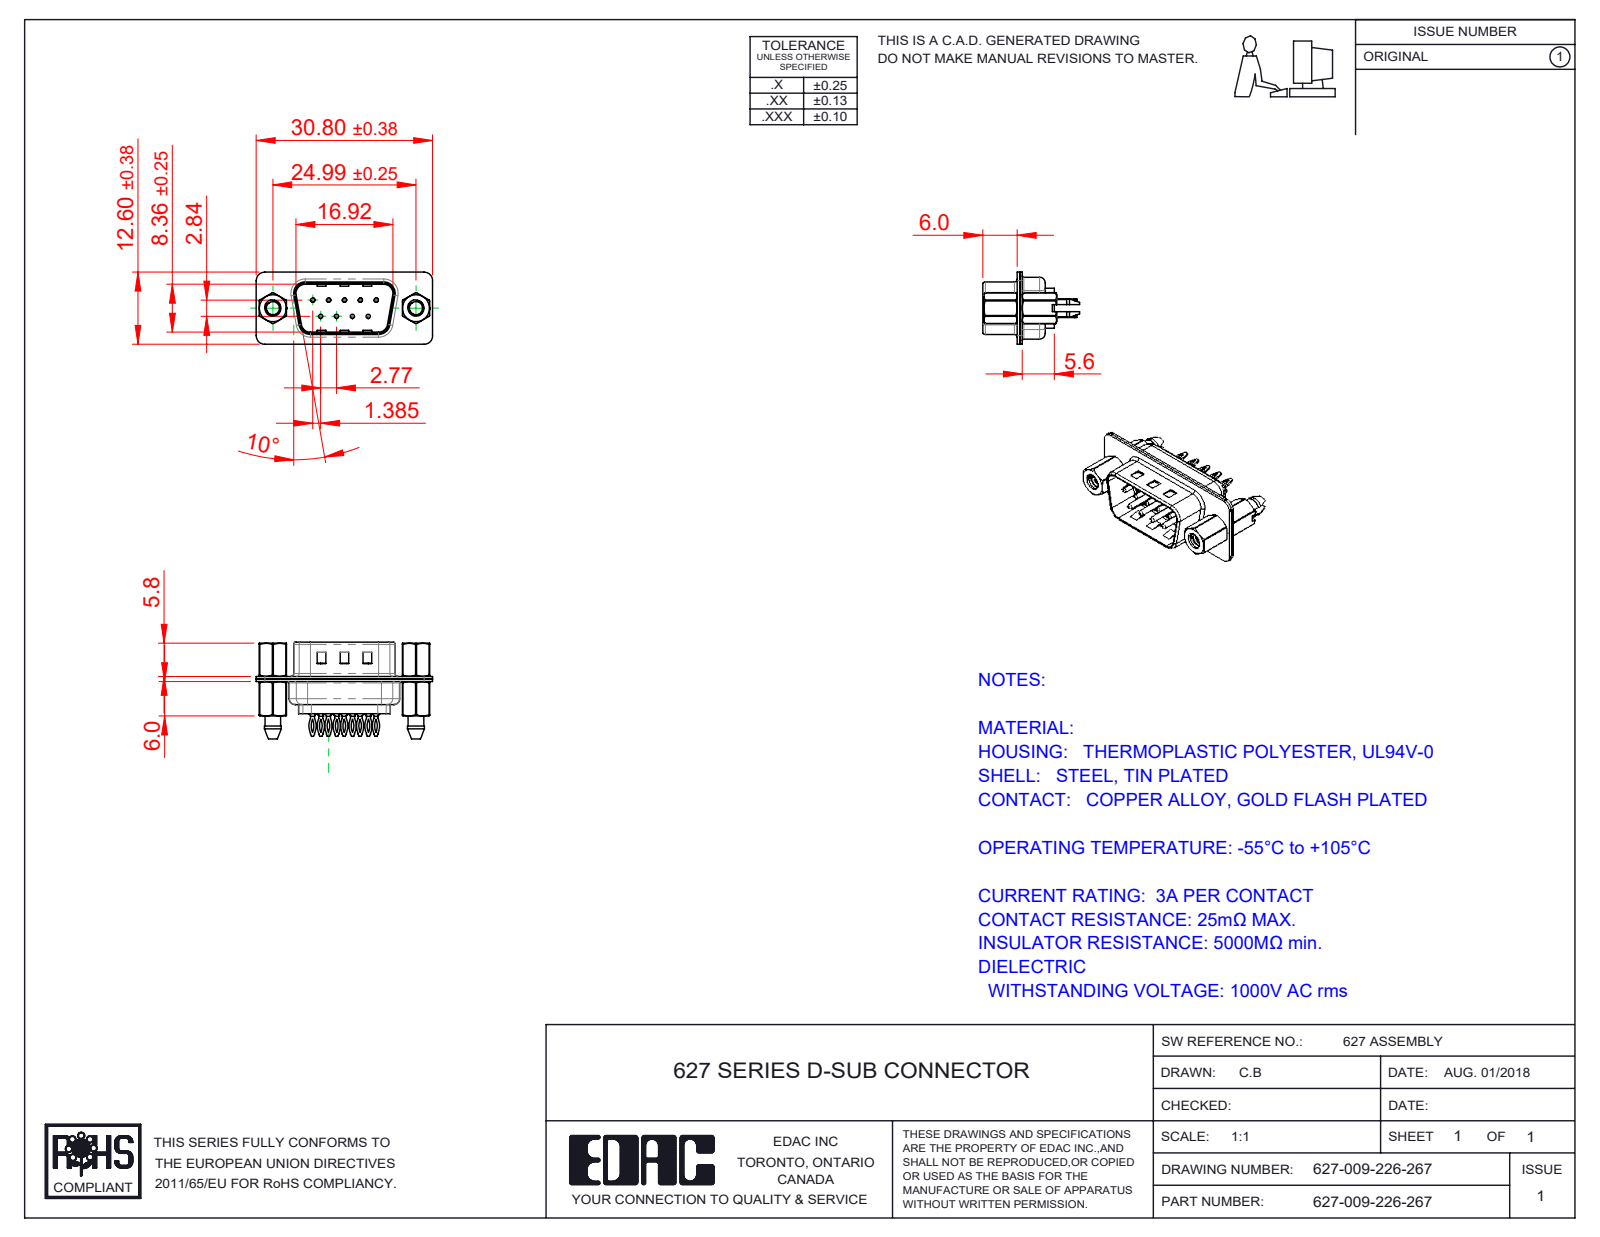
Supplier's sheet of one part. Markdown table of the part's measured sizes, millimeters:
| quantity | value |
| --- | --- |
| part name | 627 Contact Row 1_26L; 627 Contact Row 2_26L; 627 4-40 Hex Standoff; 627-009-226-267 (+4 more) |
| STEP written by | SolidWorks 2020 (CONFIG_CONTROL_DESIGN) |
| units | millimeters |
| bodies | 16 solids, 1188 faces (341 planar, 512 cylindrical, 335 other) |
| overall size | 30.8 × 16.9 × 12.6 |
| volume | 1 639 mm³ |
| surface area | 4 680 mm² |
| round holes (diameter × count) | 0.35 × 9, 1.1 × 9, 1.6 × 9, 2.26 × 2, 2.29 × 2, 4 × 2, 4.8 × 2 |
| round bosses / shafts (diameter × count) | 2 × 9, 1.5 × 9, 0.75 × 9, 4.9 × 2, 2.79 × 2 |
| partial cylindrical surfaces (radius × count) | 1.5 × 20, 2.92 × 18, 3.33 × 18, 2 × 12, 1.6 × 10, 0.5 × 8, 0.25 × 4, 0.6 × 4 |
| main face-to-face distances | 0.45, 0.4, 0.9, 0.82, 9.58, 1.4, 4.76, 8.76, 6.5, 0.5 |
| hole center spacings | 3.16, 2.77, 5.54, 5.03, 5.04, 8.31, 7.48, 7.49 |
